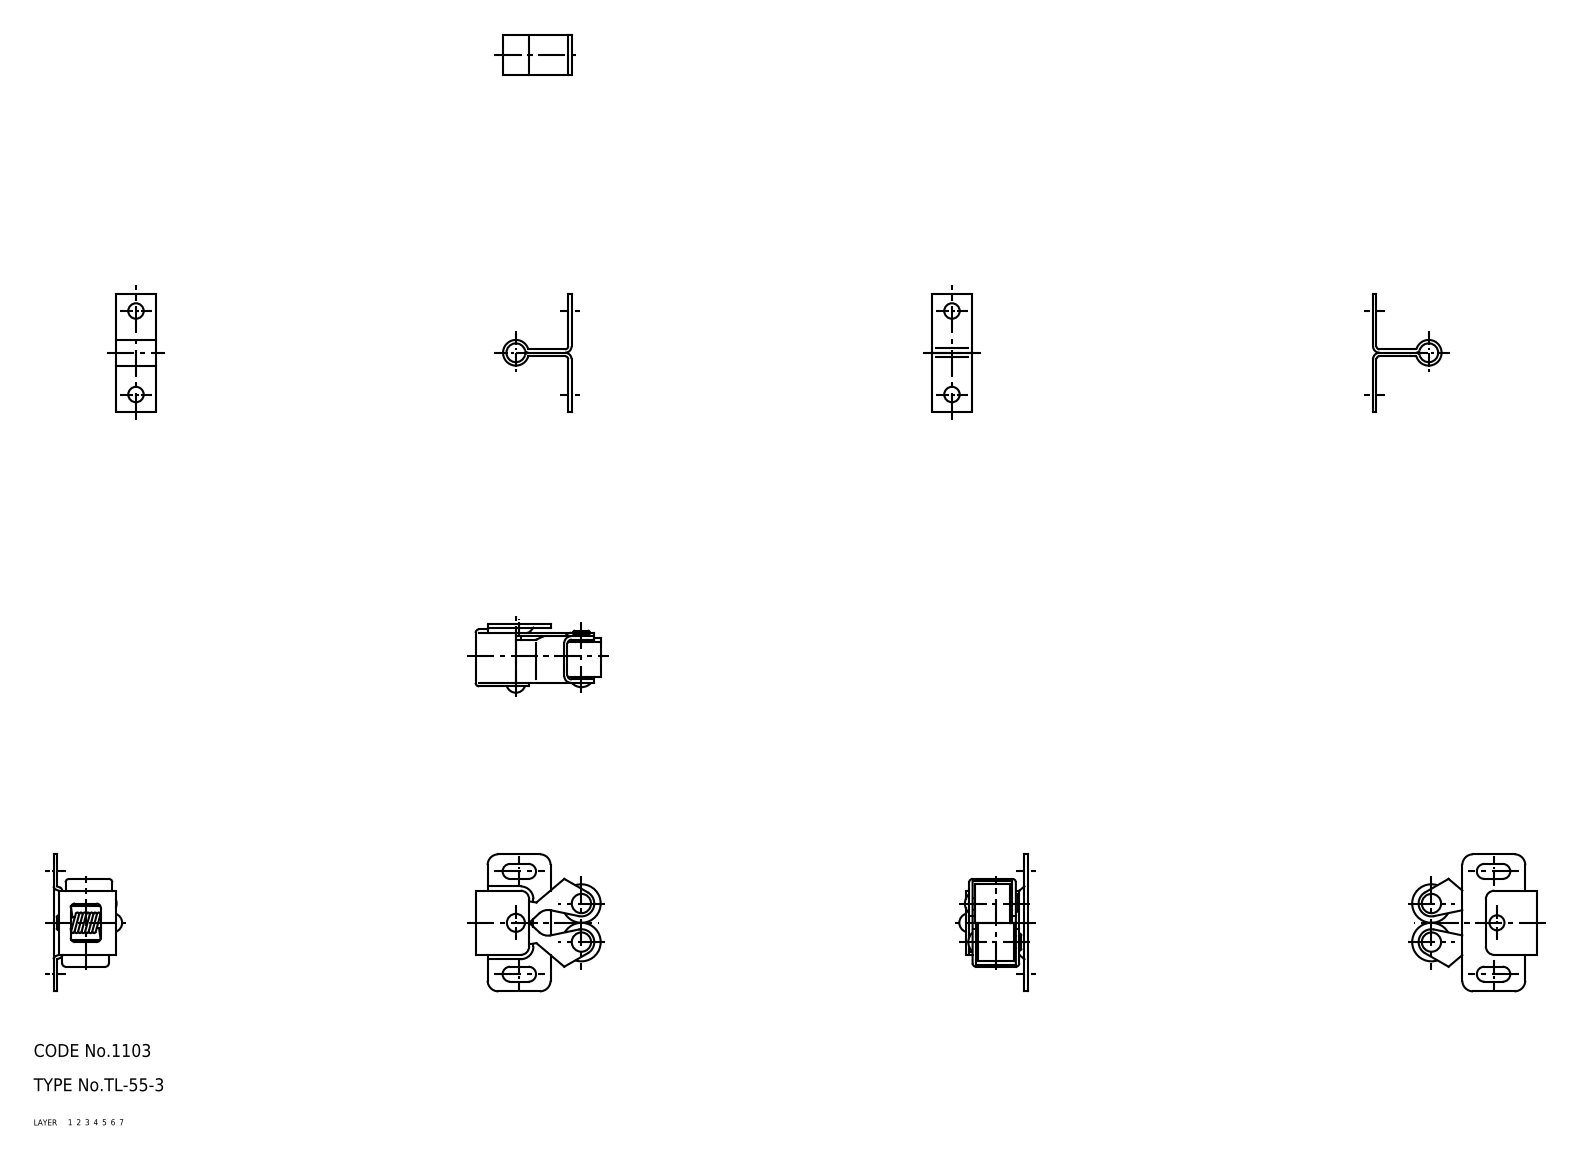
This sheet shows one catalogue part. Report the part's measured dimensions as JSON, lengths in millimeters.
{"part_name": "67124697; 67124710; 67124723; 67124736 (+6 more)", "step_written_by": "CADfix (AUTOMOTIVE_DESIGN)", "units": "millimeters", "bodies": {"solids": 10, "faces": 238, "planar": 0, "cylindrical": 0, "other": 238}, "overall_size": [55.5, 32, 16], "volume_mm3": 3010, "surface_area_mm2": 6602}
